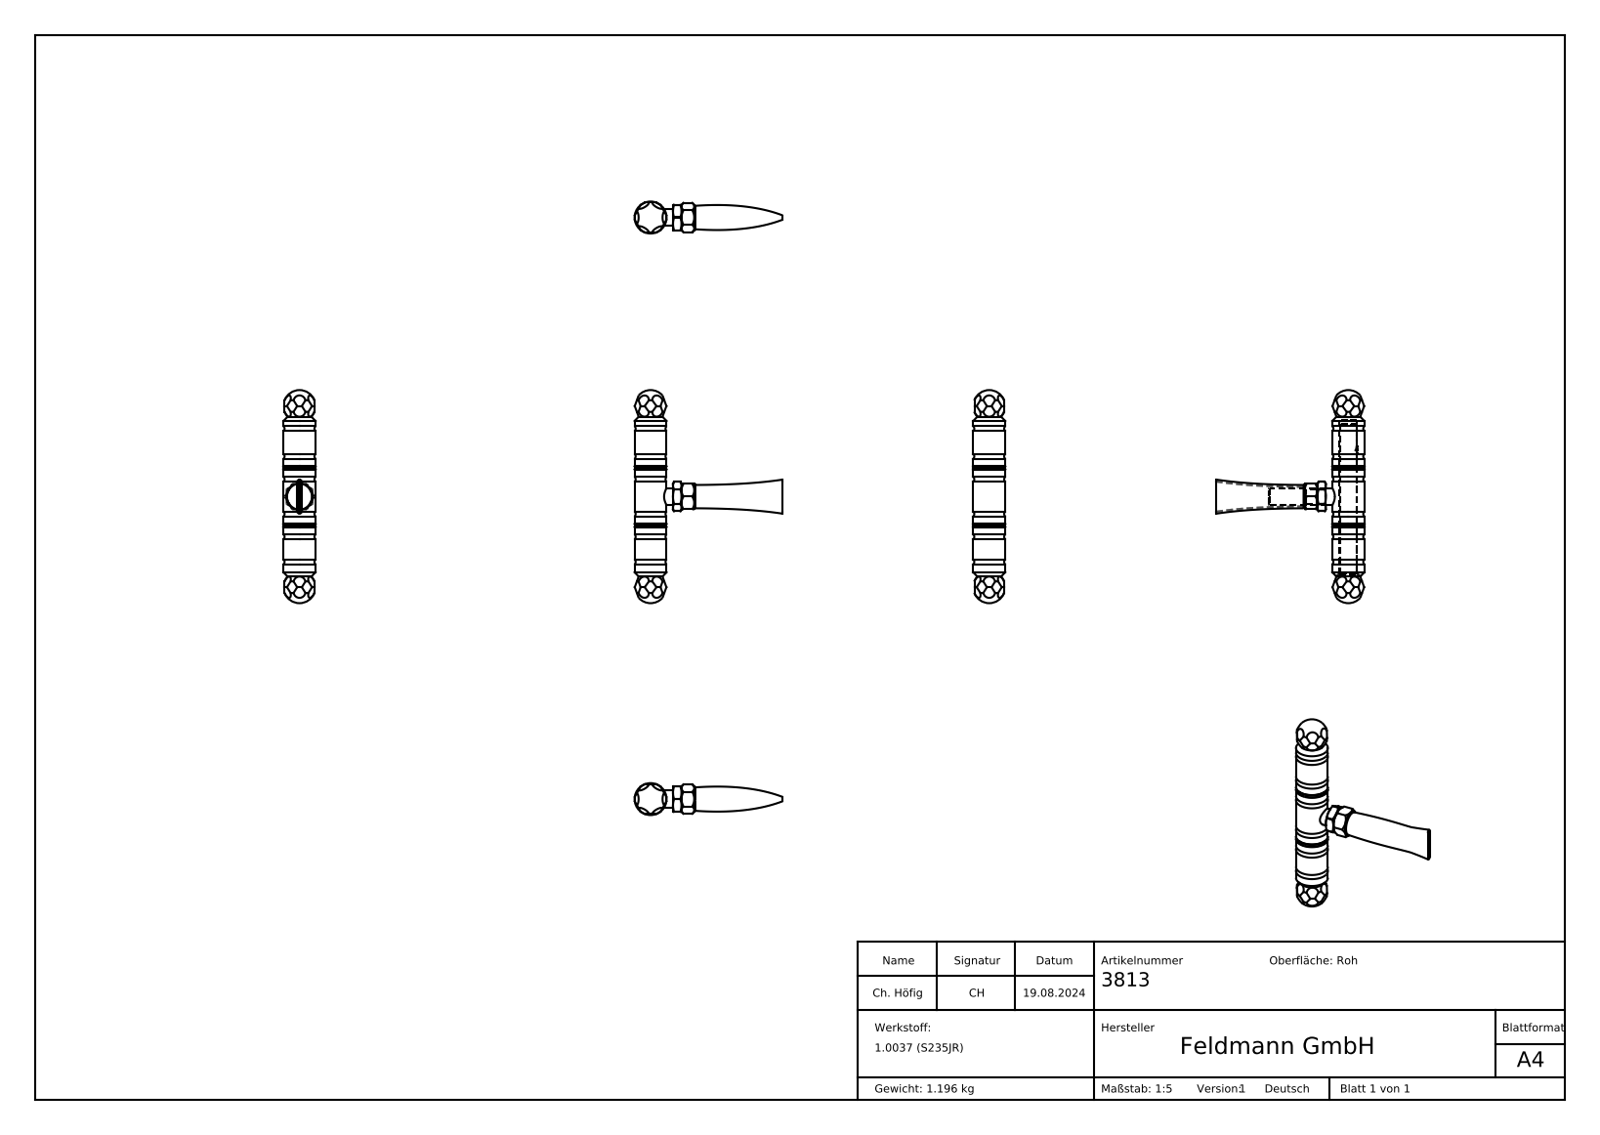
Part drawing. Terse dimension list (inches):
name: 3813 Teil1-5_3813 Teil1 Keyshot; 3813 Teil6_3813 Teil6 Keyshot; 3813; 3813 Teil1-5_3813 Teil2 Keyshot (+4 more)
written by: SolidWorks 2018 (CONFIG_CONTROL_DESIGN)
unit: in
bodies: 8 solids, 537 faces (65 planar, 130 cylindrical, 342 other)
size: 7.874 × 5.472 × 1.181
volume: 9.215 in³; area: 89.18 in²
holes: 1× ⌀0.551, 1× ⌀0.65, 1× ⌀0.689
bosses: 2× ⌀0.63, 1× ⌀1.181
rounds: 78× R0.004, 6× R0.02
face distances: 2.126, 0.079, 1.098, 2.289, 2.205, 2.047, 3.387, 1.191, 0.937, 1.811
